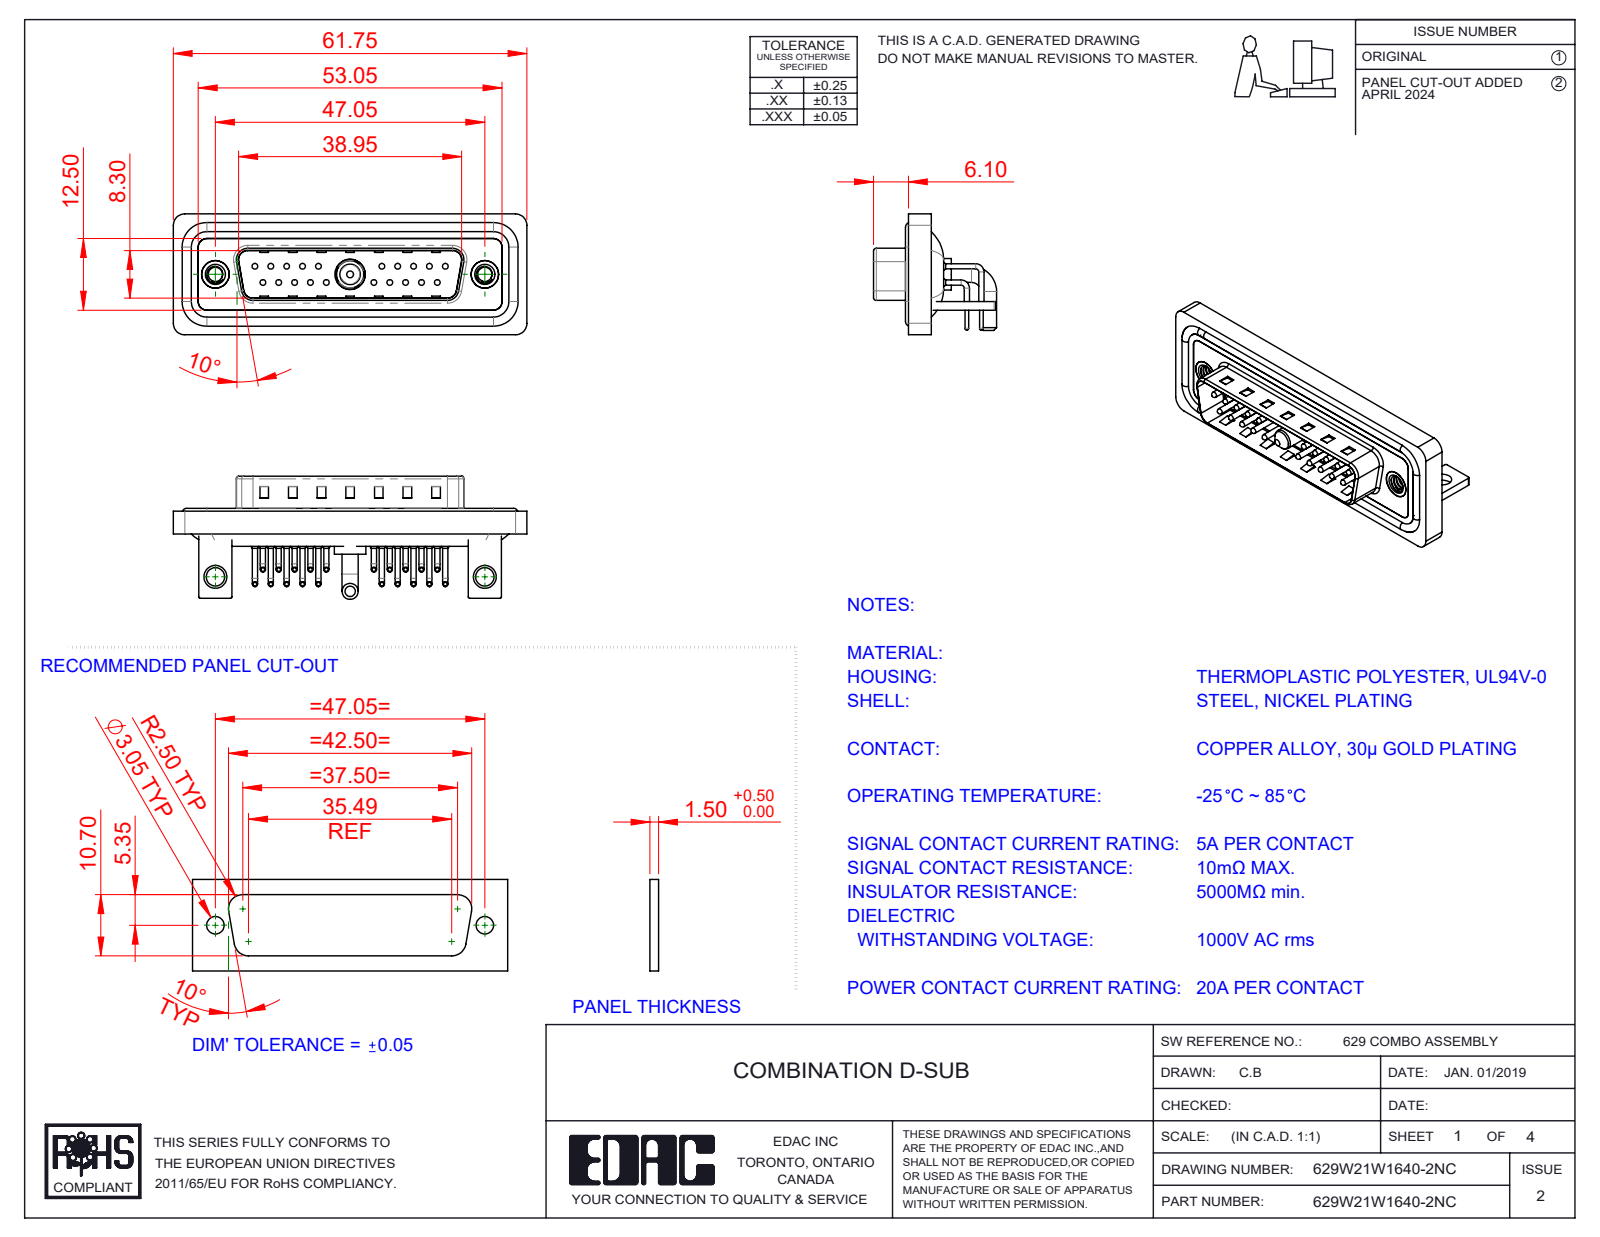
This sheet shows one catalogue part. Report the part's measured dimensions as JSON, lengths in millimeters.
{"part_name": "Power Pin_20A RA; 629W21W1640-2NC; 629Combo Contact Row 1; 629Combo Shell Front_25 Contacts (+6 more)", "step_written_by": "SolidWorks 2023 (CONFIG_CONTROL_DESIGN)", "units": "millimeters", "bodies": {"solids": 31, "faces": 2764, "planar": 1519, "cylindrical": 947, "other": 298}, "overall_size": [61.75, 21.5, 21.1], "volume_mm3": 7690, "surface_area_mm2": 13309, "round_holes": [[0.75, 20], [1.6, 20], [2, 20], [2.5, 2], [3.2, 2], [4, 2], [4.8, 2], [5, 2], [4.85, 1], [5.3, 1]], "round_bosses_or_shafts": [[0.9, 40], [1.5, 20], [1, 20], [0.65, 20], [1.6, 4], [4.9, 2], [2.8, 2], [5.5, 1]], "partial_cylinders_radius": [[1.01, 20], [2, 19], [1.5, 18], [0.25, 16], [0.5, 9], [1.6, 8], [0.6, 4], [0.65, 4]], "face_to_face_distances": [0.4, 0.8, 2.1, 2.9, 1.5, 1.1, 4.1, 1.6, 4.5, 3.7], "hole_center_spacings": [3.16, 2.77, 5.54, 8.31, 5.04, 19.39, 20.97, 22.16]}
